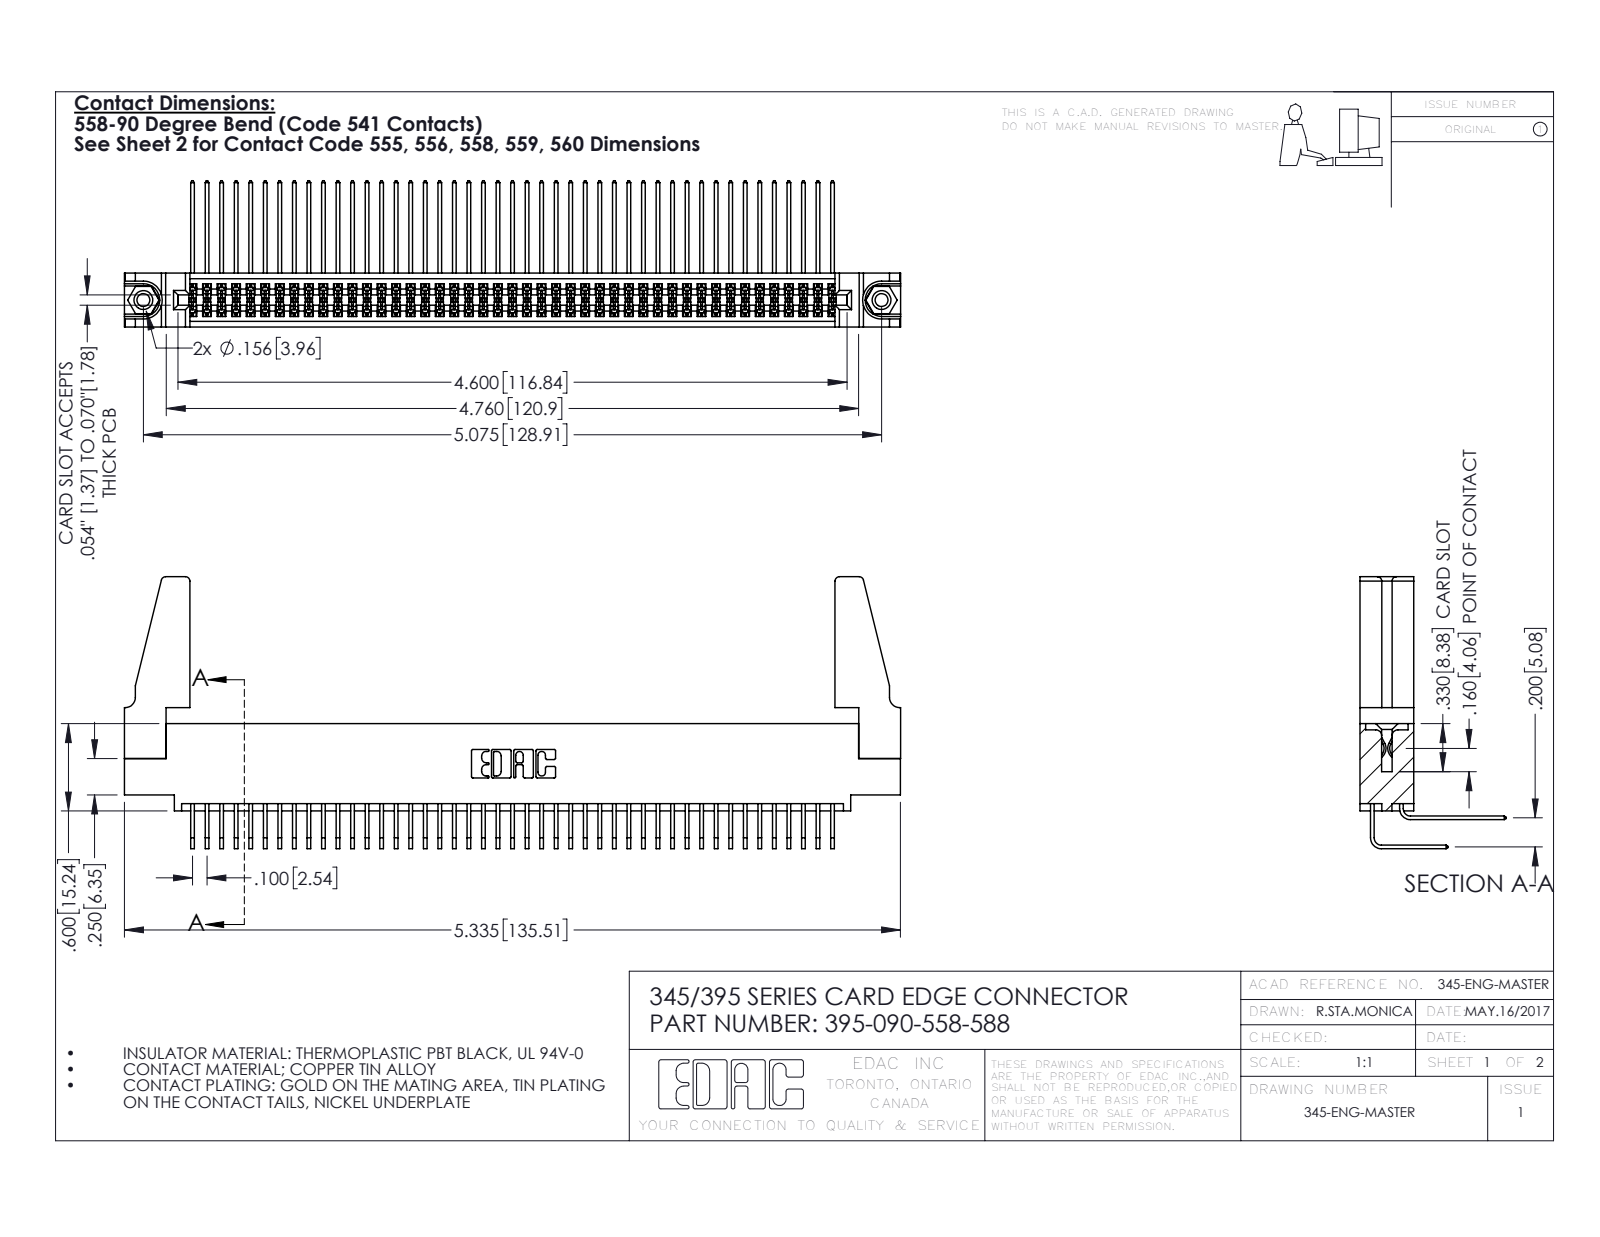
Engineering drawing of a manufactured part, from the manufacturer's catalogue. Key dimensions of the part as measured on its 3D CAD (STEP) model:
Part name (STEP PRODUCT): 395-090-558-588; 345-292-001_558 Tail - 2; 345-292-001_558 559 Tail - 1; 345 Part_0.110 Offset - 0.156 Dia-TH (+2 more)
STEP written by: SolidWorks 2016 (CONFIG_CONTROL_DESIGN)
Units: inches
Bodies: 95 solids, 4934 faces (3306 planar, 1612 cylindrical, 16 other)
Overall size (bounding box): 5.336 × 1.869 × 1.005
Volume: 1.031 in³ · Surface area: 40.11 in²
Round holes (diameter × count): ⌀0.089 ×2, ⌀0.125 ×2, ⌀0.156 ×2, ⌀0.064 ×1
Round bosses / shafts (diameter × count): ⌀0.155 ×2
Partial cylindrical surfaces — rounded edges, fillets, slot ends (radius × count): R0.006 ×136, R0.01 ×22, R0.03 ×8, R0.007 ×6, R0.031 ×6, R0.026 ×3, R0.014 ×2, R0.019 ×2
Main face-to-face distances: 0.072, 0.298, 0.2, 0.37, 0.098, 0.272, 0.025, 0.225, 0.025, 0.175
Hole centre spacings: 0.27, 4.839, 5.075
